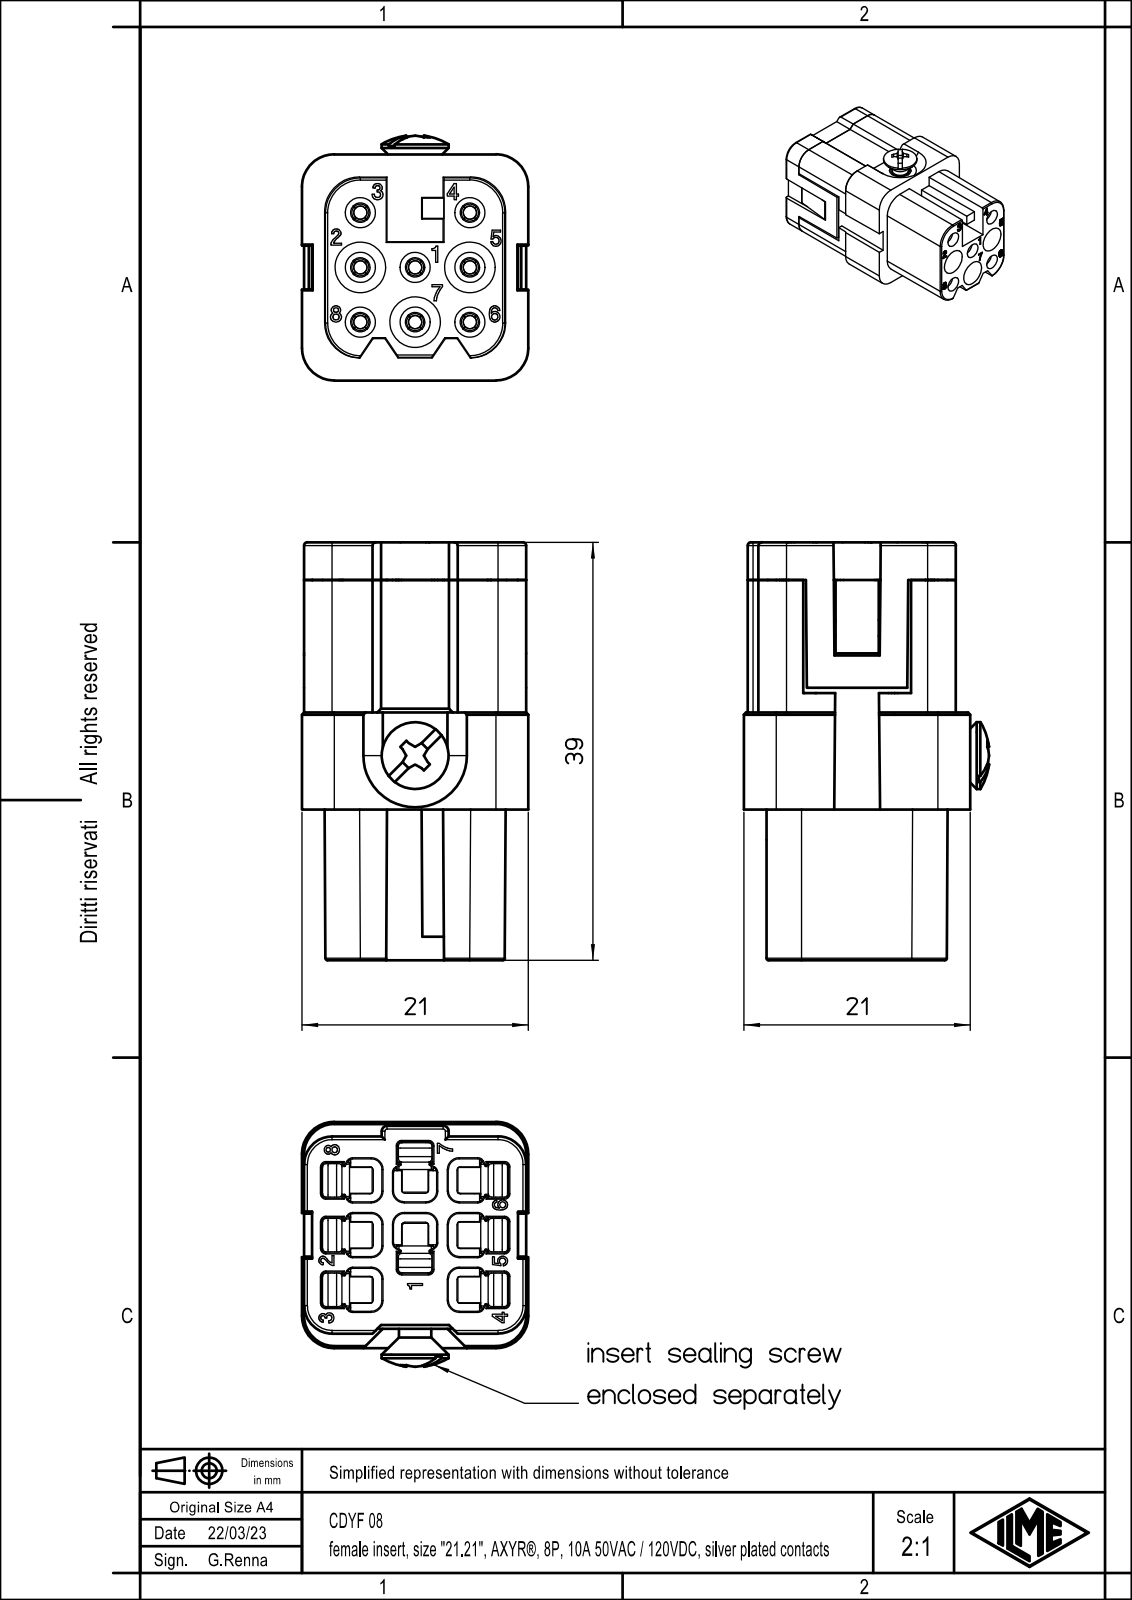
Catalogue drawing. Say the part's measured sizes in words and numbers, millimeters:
The part is named "CDYF 08". Its 3-D file was written by "Creo Elements/Direct Modeling 20.1B 02-Apr-2019 (C) Parametric Technology GmbH (AUTOMOTIVE_DESIGN)". It is 1 solid with 1613 faces: 920 planar, 406 cylindrical and 287 other. Overall it measures 38.8 by 22.72 by 21 millimeters. Its volume is 11 694 cubic millimeters and its surface area 7 367 square millimeters. Round holes: 8 of diameter 1.7, 8 of diameter 1.8, 5 of diameter 2.8, 3 of diameter 4.7, 1 of diameter 2.5, 1 of diameter 4. Round bosses or shafts: 8 of diameter 2.5, 1 of diameter 6.2, 1 of diameter 3.8, 1 of diameter 3. Partial cylindrical surfaces (rounded edges, fillets, slot ends): 58 of radius 0.1, 39 of radius 0.3, 30 of radius 0.2, 26 of radius 0.5, 16 of radius 0.4, 16 of radius 1, 4 of radius 1.5, 4 of radius 2.6. The main face-to-face distances are 0.8, 1, 19.8, 20.8, 24.8, 21.3, 3.5, 1.35, 20, 19.65. The hole center spacings are 5.08, 7.18, 11.36, 10.16, 14.37.
